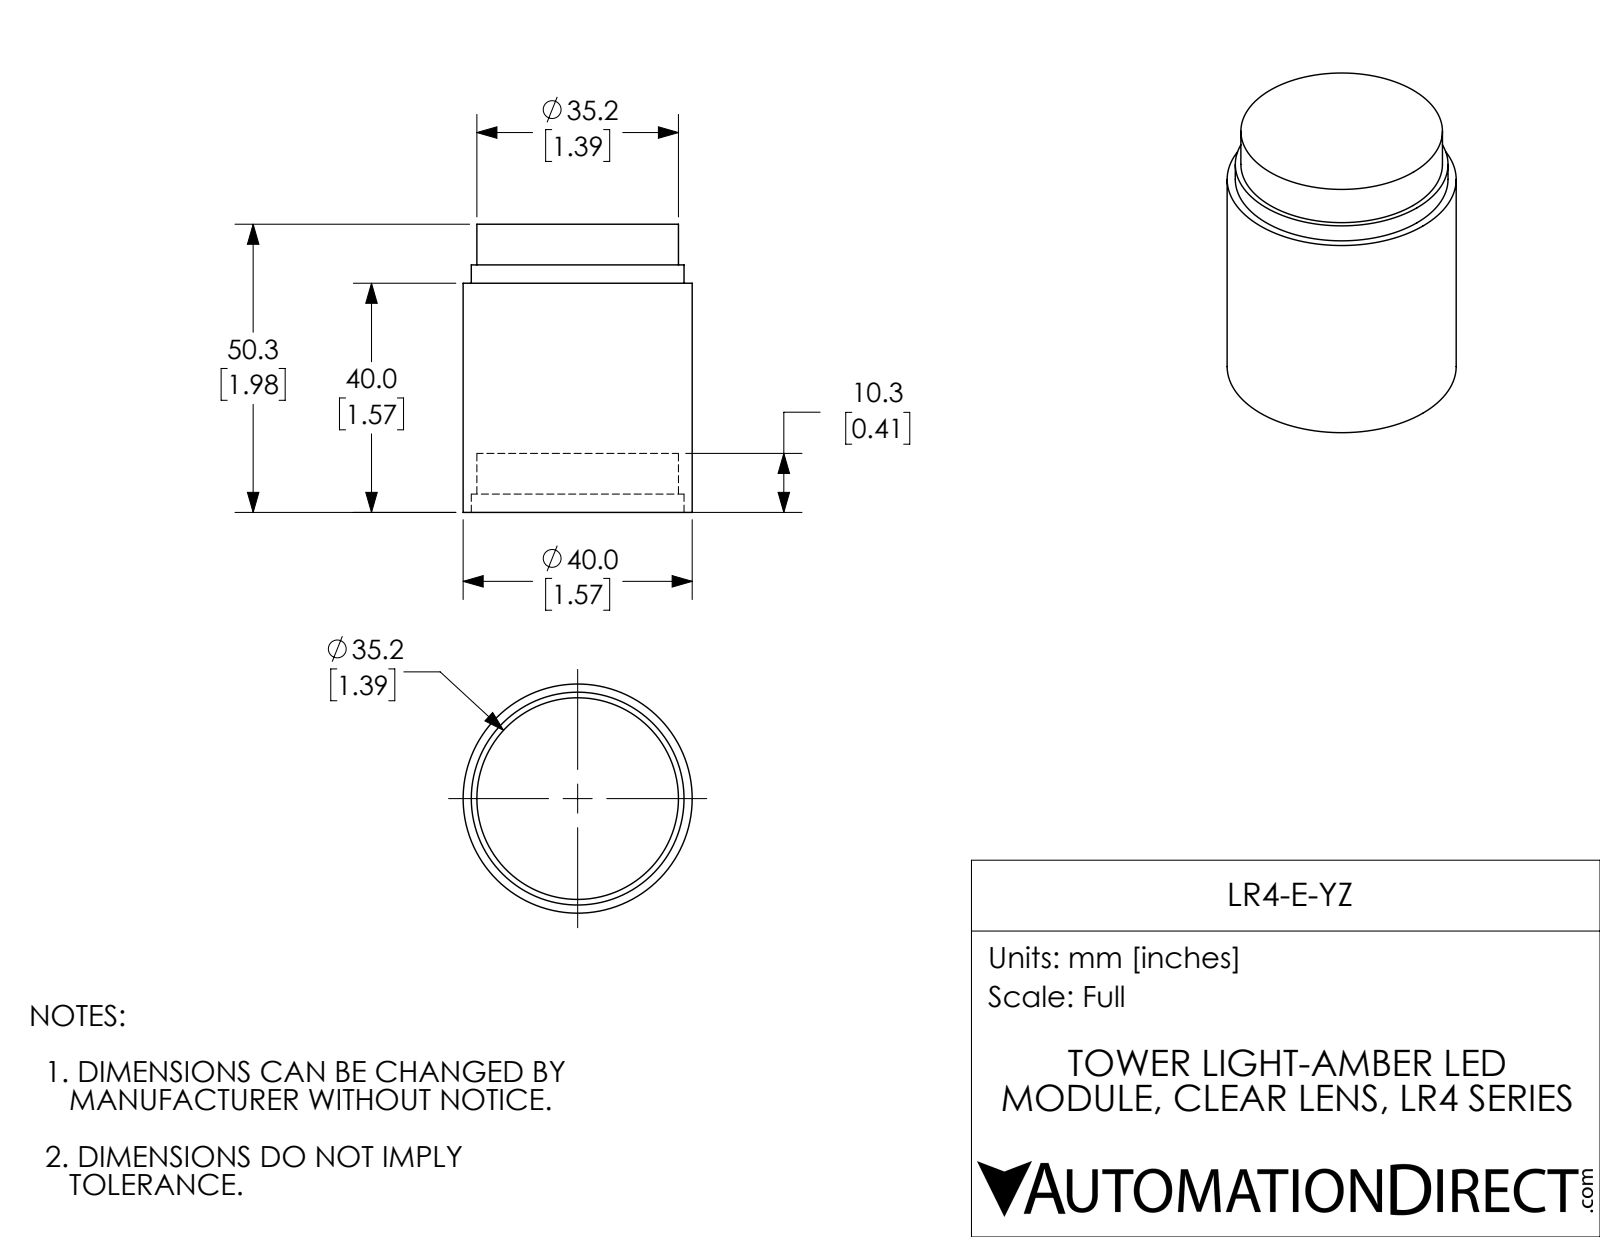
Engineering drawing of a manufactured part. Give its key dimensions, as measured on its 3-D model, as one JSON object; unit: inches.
{"part_name": "LR4-E-YZ", "step_written_by": "SolidWorks 2017 (AUTOMOTIVE_DESIGN)", "units": "inches", "bodies": {"solids": 1, "faces": 16, "planar": 6, "cylindrical": 10, "other": 0}, "overall_size": [1.98, 1.575, 1.575], "volume_in3": 3.067, "surface_area_in2": 15.28, "round_holes": [[1.386, 1], [1.463, 1]], "round_bosses_or_shafts": [[1.575, 1]], "face_to_face_distances": [1.575, 0.406, 0.126, 0.28, 1.98, 1.169, 1.701, 1.295, 1.449, 1.854]}
